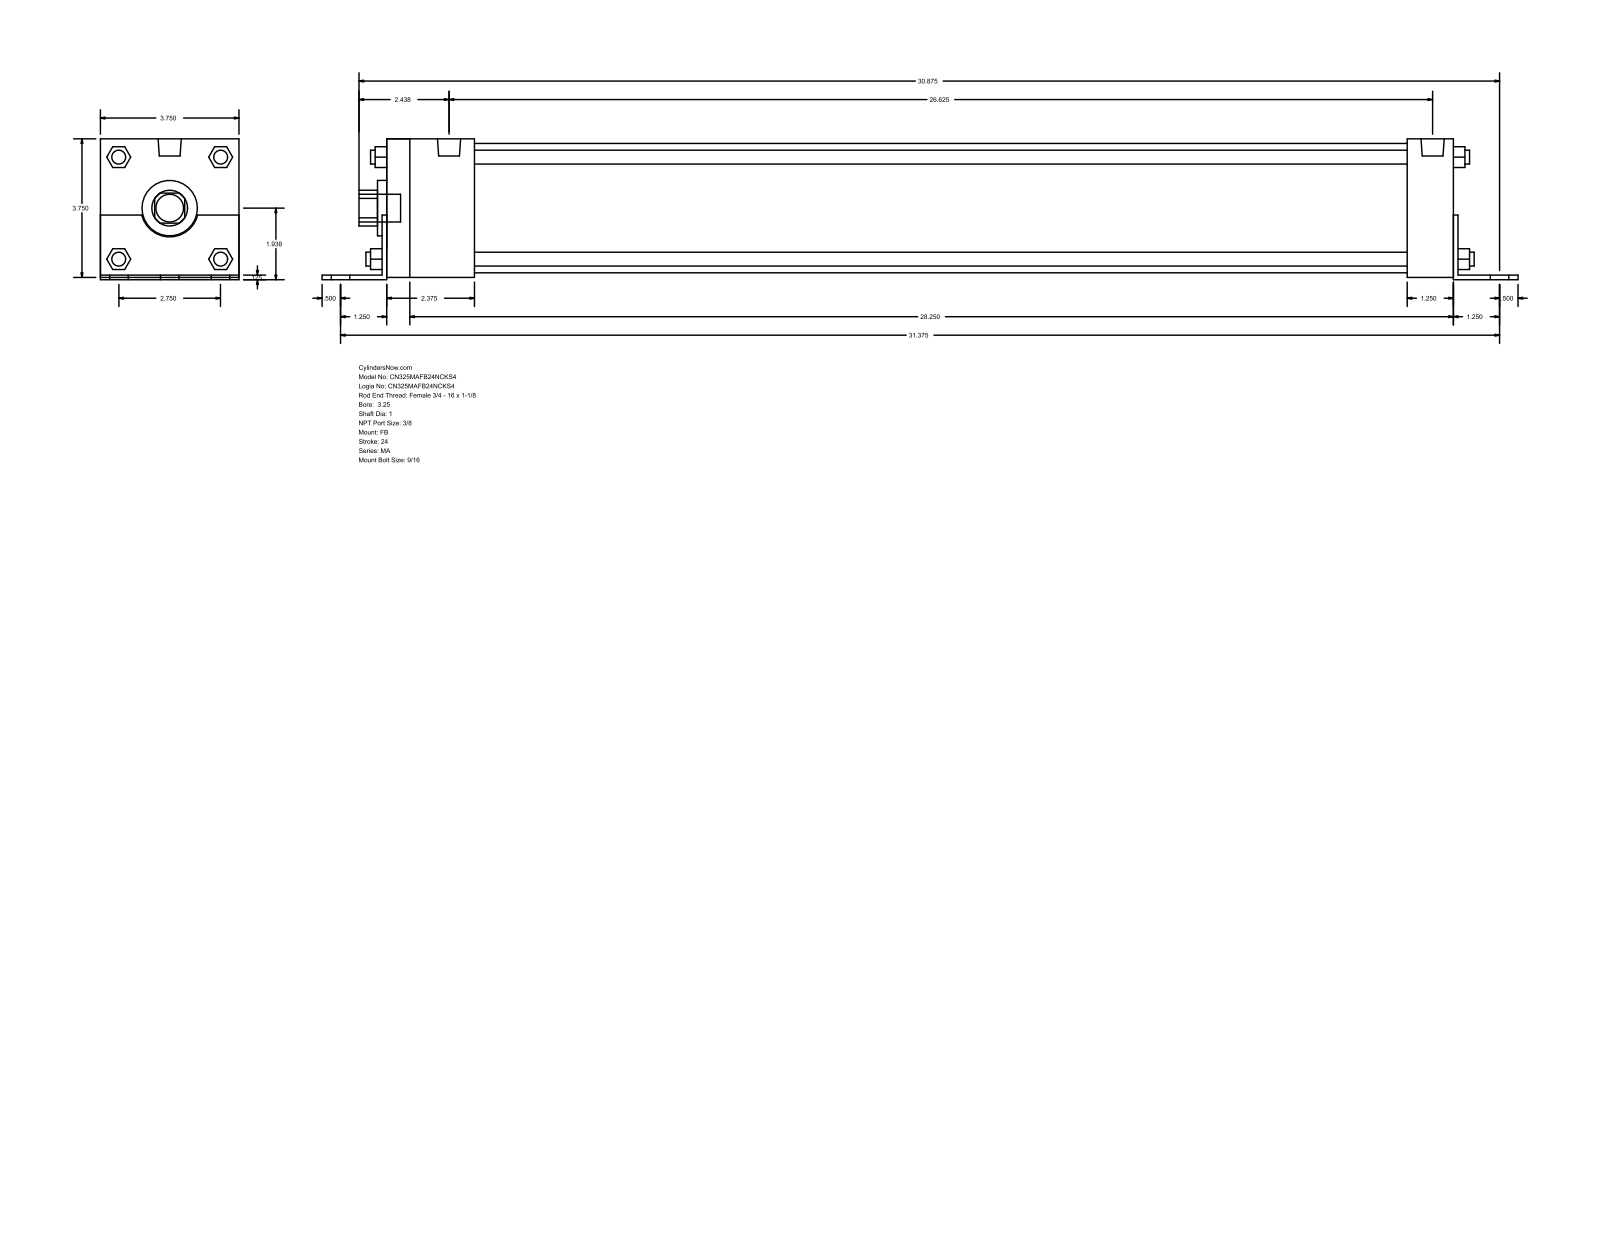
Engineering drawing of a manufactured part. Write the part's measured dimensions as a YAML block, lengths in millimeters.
part_name: "MA_FB__0325_1"
step_written_by: "GSSL Pune (CONFIG_CONTROL_DESIGN)"
units: millimeters
bodies: {solids: 0, faces: 140, planar: 105, cylindrical: 35, other: 0}
overall_size: [822.33, 96.84, 95.25]
round_holes:
  - {diameter: 25.4, count: 1}
  - {diameter: 38.1, count: 1}
  - {diameter: 88.9, count: 1}
round_bosses_or_shafts:
  - {diameter: 14.29, count: 6}
  - {diameter: 11.11, count: 4}
  - {diameter: 9.53, count: 4}
  - {diameter: 15.93, count: 2}
  - {diameter: 19.05, count: 1}
partial_cylinders:
  - {radius: 12.29, count: 1}
  - {radius: 19.81, count: 1}
face_to_face_distances: [95.24, 3.17, 1.59, 96.83, 1.58, 93.66, 736.6, 733.43, 739.77, 704.85]
